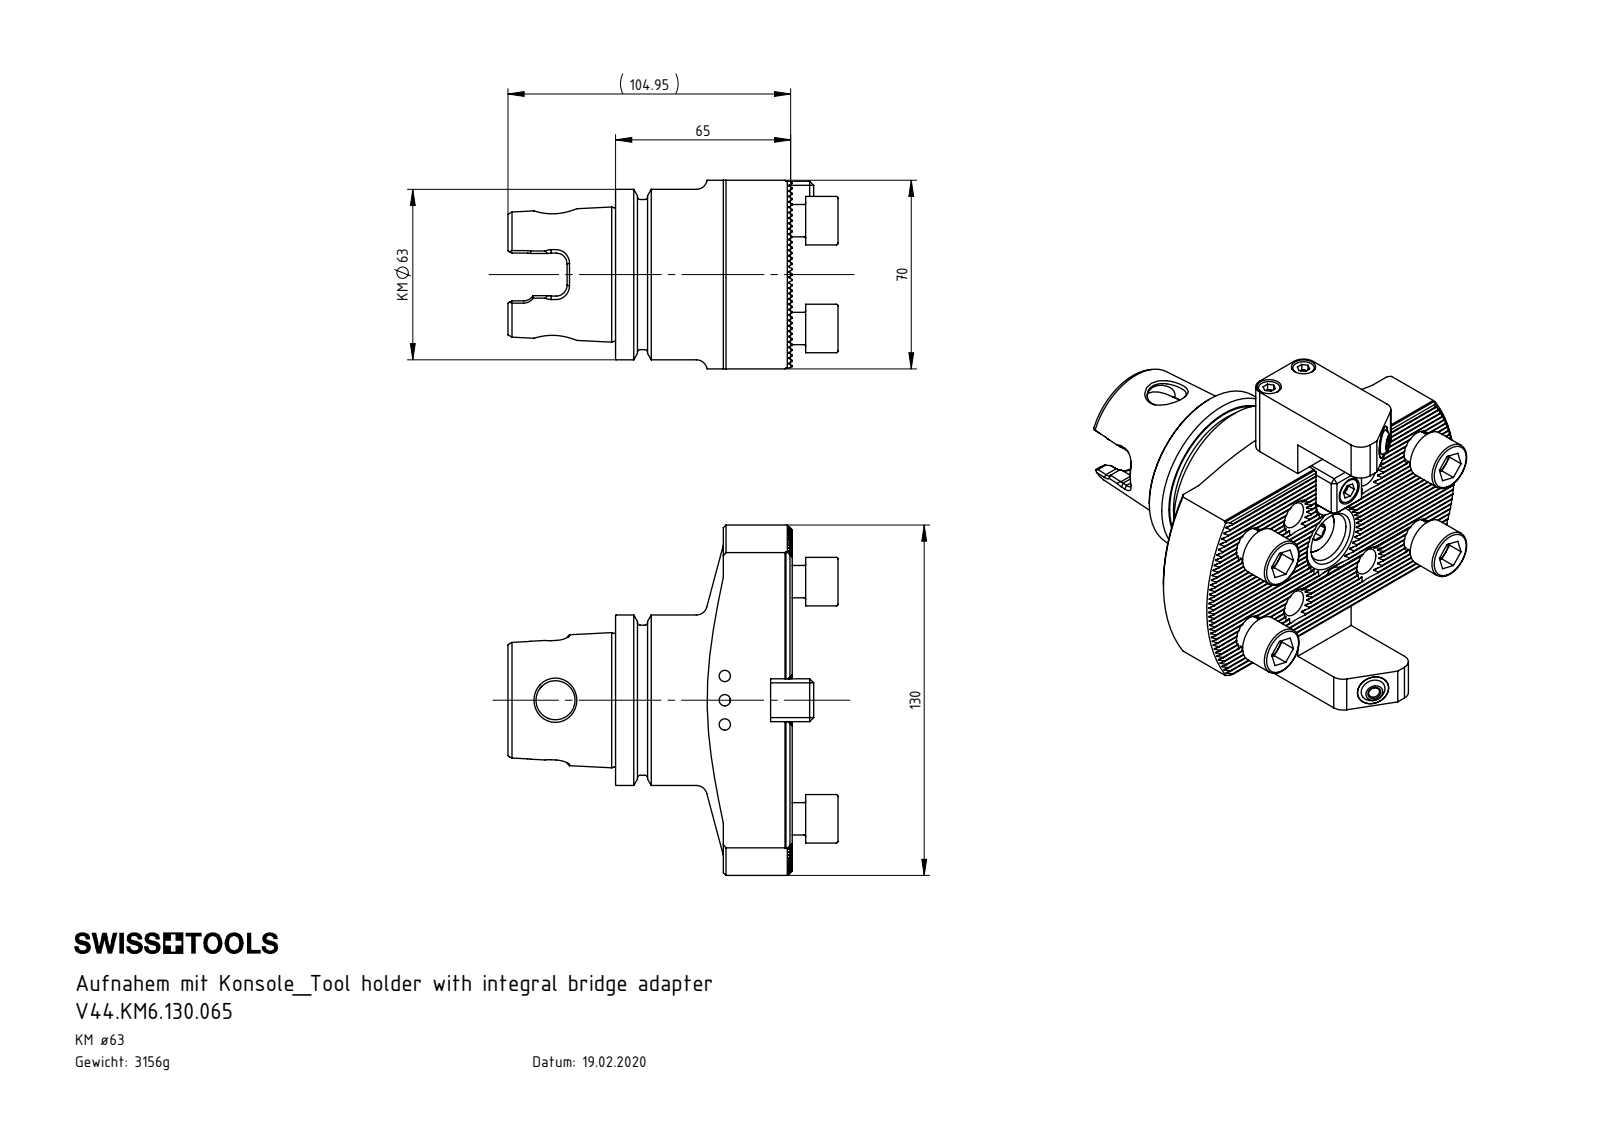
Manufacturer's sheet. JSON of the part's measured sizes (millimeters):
{"part_name": "ISO 4762 - M6 x 16; Ko1-ER1.001.016_A; ISO 4762 - M12 x 25; KM6.Ko1.K21.065 (+2 more)", "step_written_by": "SolidWorks 2017 (AUTOMOTIVE_DESIGN)", "units": "millimeters", "bodies": {"solids": 8, "faces": 784, "planar": 489, "cylindrical": 163, "other": 132}, "overall_size": [130, 122.53, 70], "volume_mm3": 382223, "surface_area_mm2": 69977, "round_holes": [[10.2, 9], [4.2, 3], [10.5, 2], [5, 1], [6.5, 1], [7.24, 1], [14.5, 1], [19, 1], [31.1, 1], [35.08, 1], [36.5, 1]], "round_bosses_or_shafts": [[12, 5], [18, 4], [63.25, 1], [55.7, 1], [17, 1], [10, 1], [6, 1]], "partial_cylinders_radius": [[0.14, 34], [4, 6], [6.85, 2], [7.95, 1], [65, 1]], "face_to_face_distances": [1.73, 17.32, 70, 8.66, 3.46, 5.2, 6.93, 15.59, 19.05, 3.47], "hole_center_spacings": [25, 27.59, 40, 47.17, 48.33, 63, 74.63, 9]}
